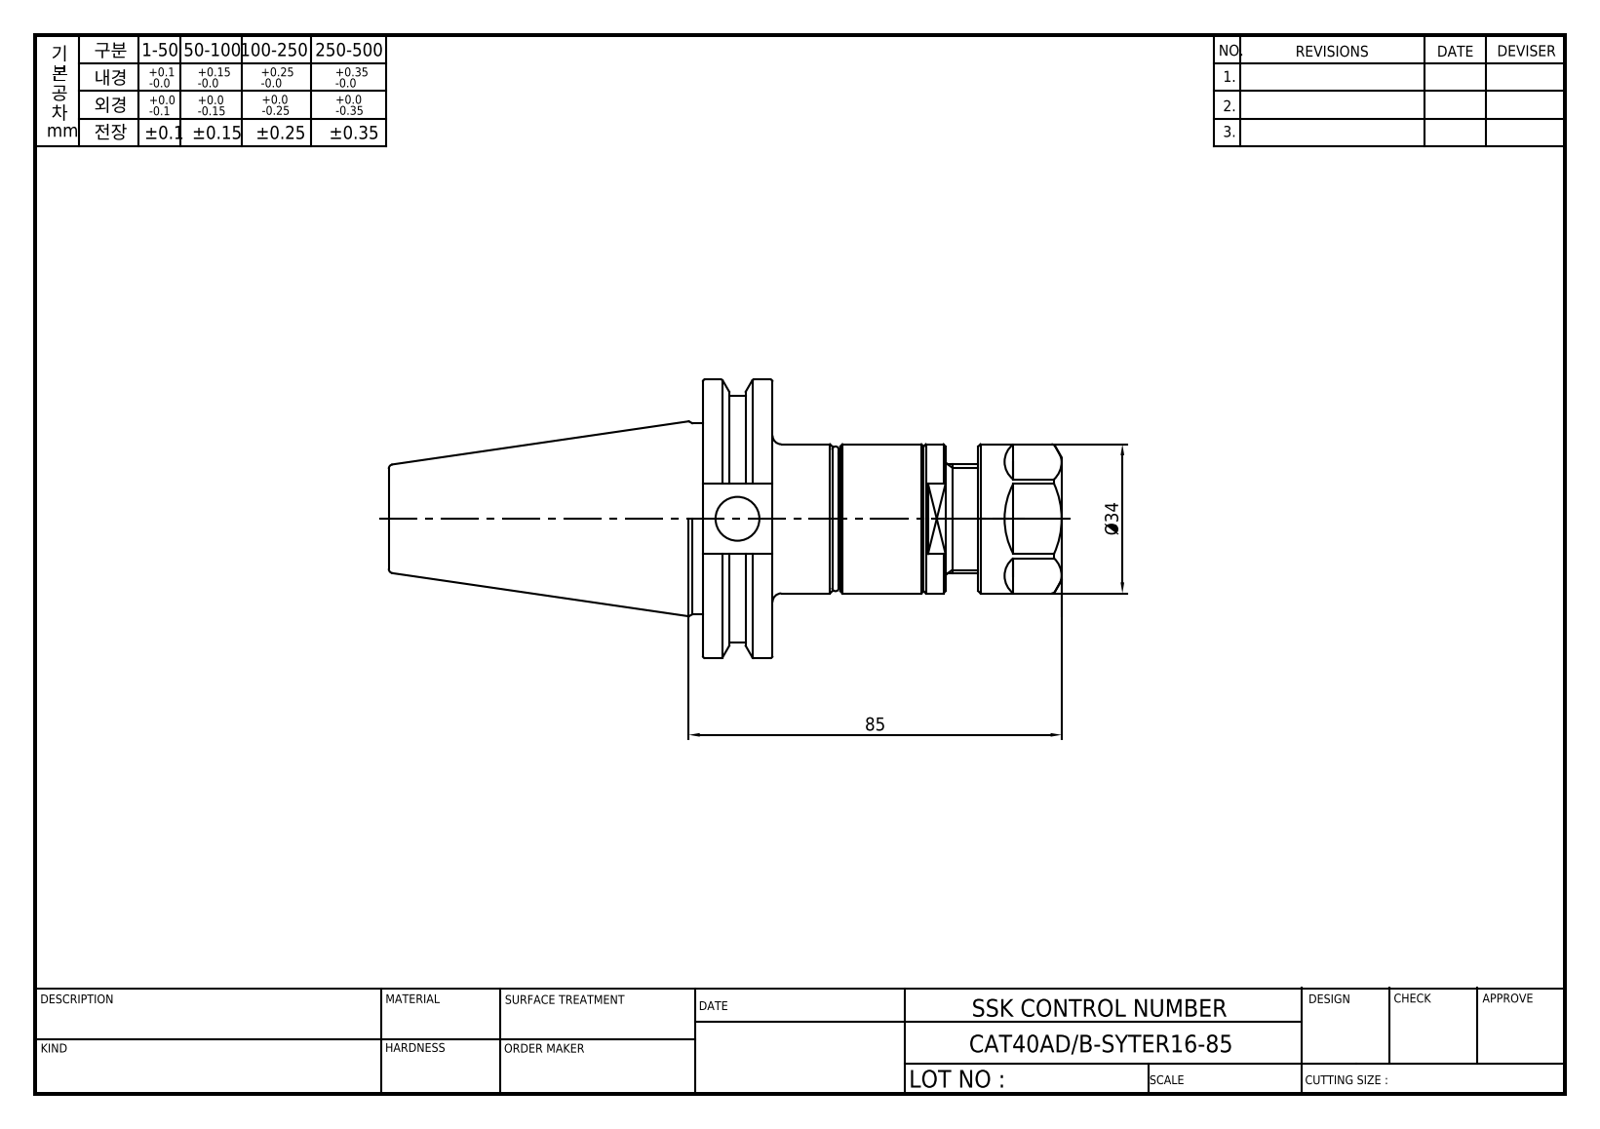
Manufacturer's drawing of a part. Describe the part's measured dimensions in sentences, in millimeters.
The part is named "CAT40ADB-SYTER16-85; SYNCHRO-ER20-31; SYTER16-COVER(BLUE); ER20NUT". Its 3-D file was written by "Autodesk Inventor 2020 (AUTOMOTIVE_DESIGN)". It is 4 solids with 208 faces: 81 planar, 66 cylindrical and 61 other. Overall it measures 153.25 by 63.5 by 61.09 millimeters. Its volume is 143 160 cubic millimeters and its surface area 42 168 square millimeters. Round holes: 6 of diameter 4, 4 of diameter 3.24, 4 of diameter 4.1, 2 of diameter 4.2, 1 of diameter 3, 1 of diameter 4.3, 1 of diameter 5.2, 1 of diameter 5.5, 1 of diameter 9.53, 1 of diameter 10, 1 of diameter 10.2, 1 of diameter 10.6. Round bosses or shafts: 1 of diameter 63.5, 1 of diameter 43.6, 1 of diameter 34, 1 of diameter 30, 1 of diameter 28.3, 1 of diameter 25, 1 of diameter 23.6, 1 of diameter 9.8. Partial cylindrical surfaces (rounded edges, fillets, slot ends): 1 of radius 28.15. The main face-to-face distances are 15.88, 30, 31.63, 15.75, 31.2, 19, 81.83, 65.95, 50.2, 33.3. The hole center spacings are 8.45, 11.95, 16.9.
